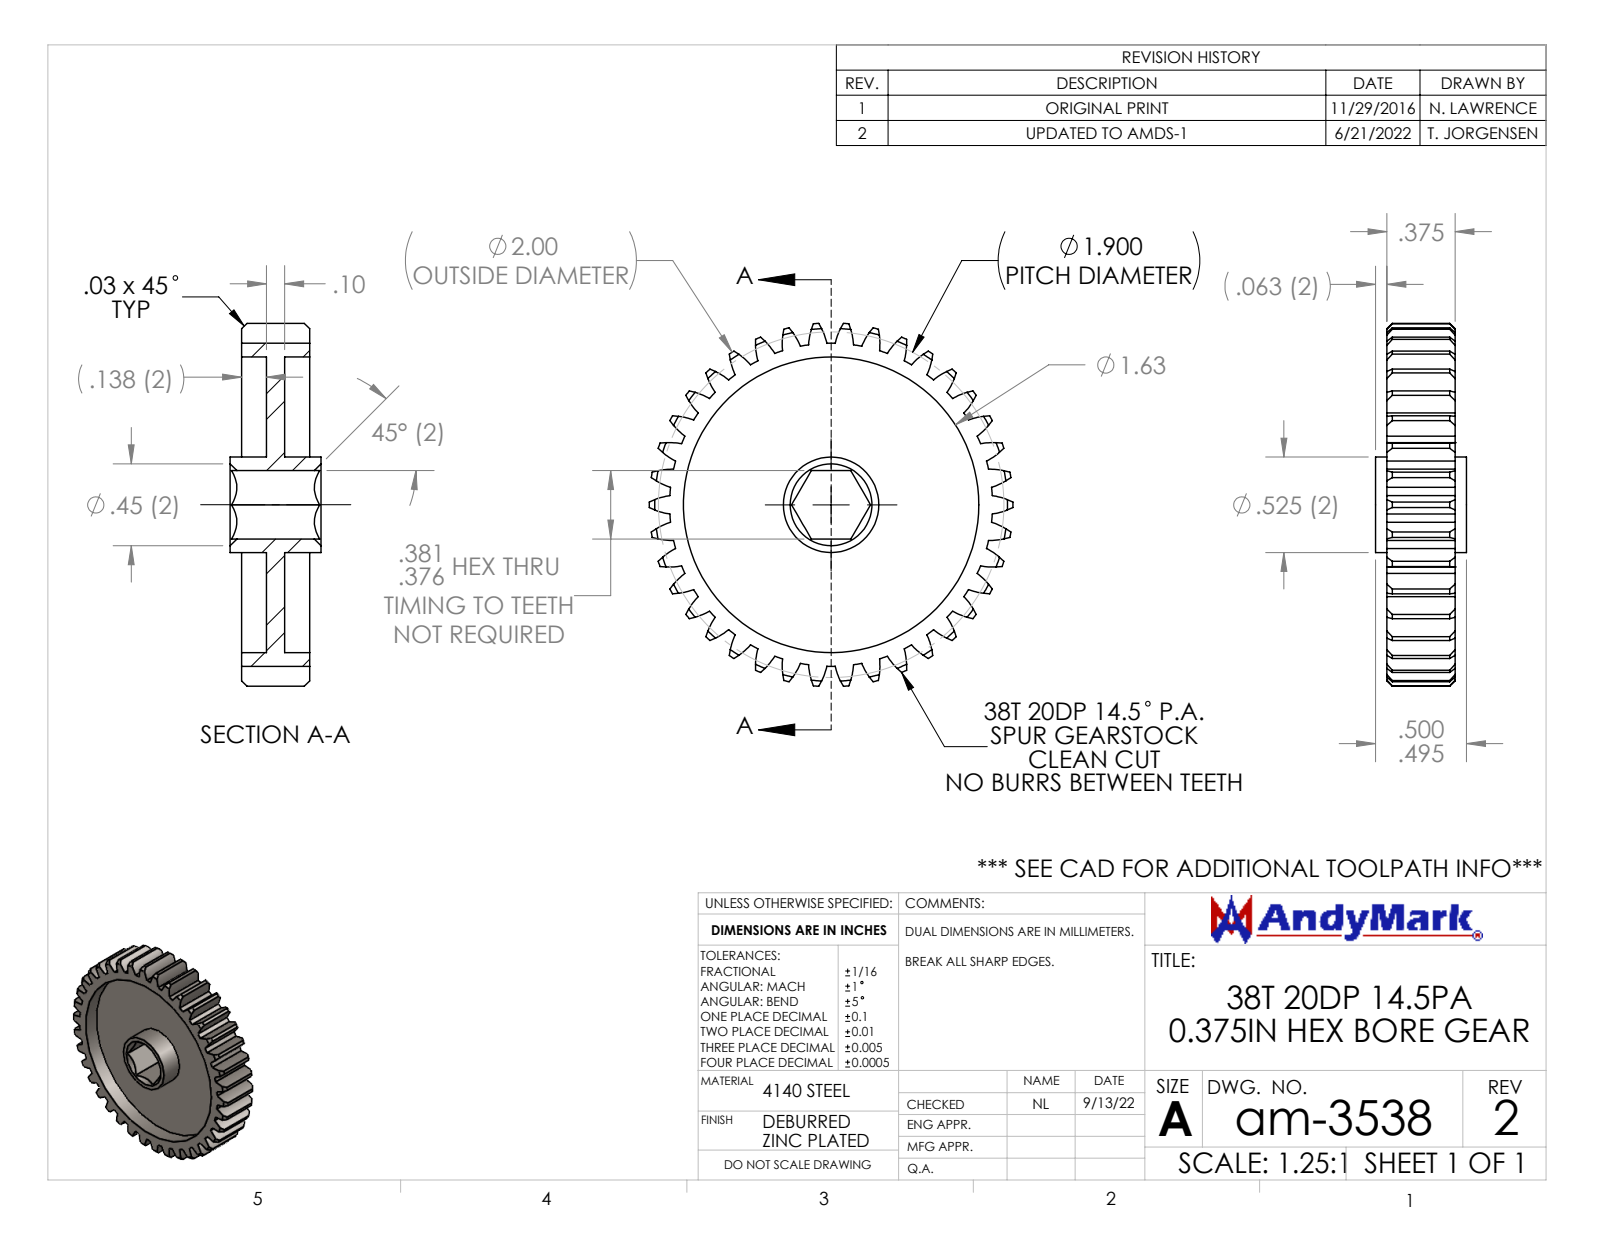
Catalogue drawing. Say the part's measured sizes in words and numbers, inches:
The part is named "am-3538 38T 20DP 375Hex 375 FW". Its 3-D file was written by "SolidWorks 2021 (CONFIG_CONTROL_DESIGN)". It is 1 solid with 257 faces: 12 planar, 165 cylindrical and 80 other. Overall it measures 2 by 1.995 by 0.5 inches. Its volume is 0.497 cubic inches and its surface area 12.38 square inches. Round holes: 1 of diameter 1.625. Round bosses or shafts: 1 of diameter 0.525. Partial cylindrical surfaces (rounded edges, fillets, slot ends): 76 of radius 0.38, 1 of radius 0.888, 1 of radius 1. The main face-to-face distances are 0.1, 0.137, 0.237, 0.375, 0.238, 0.138, 0.376, 0.2, 0.3, 0.063.
